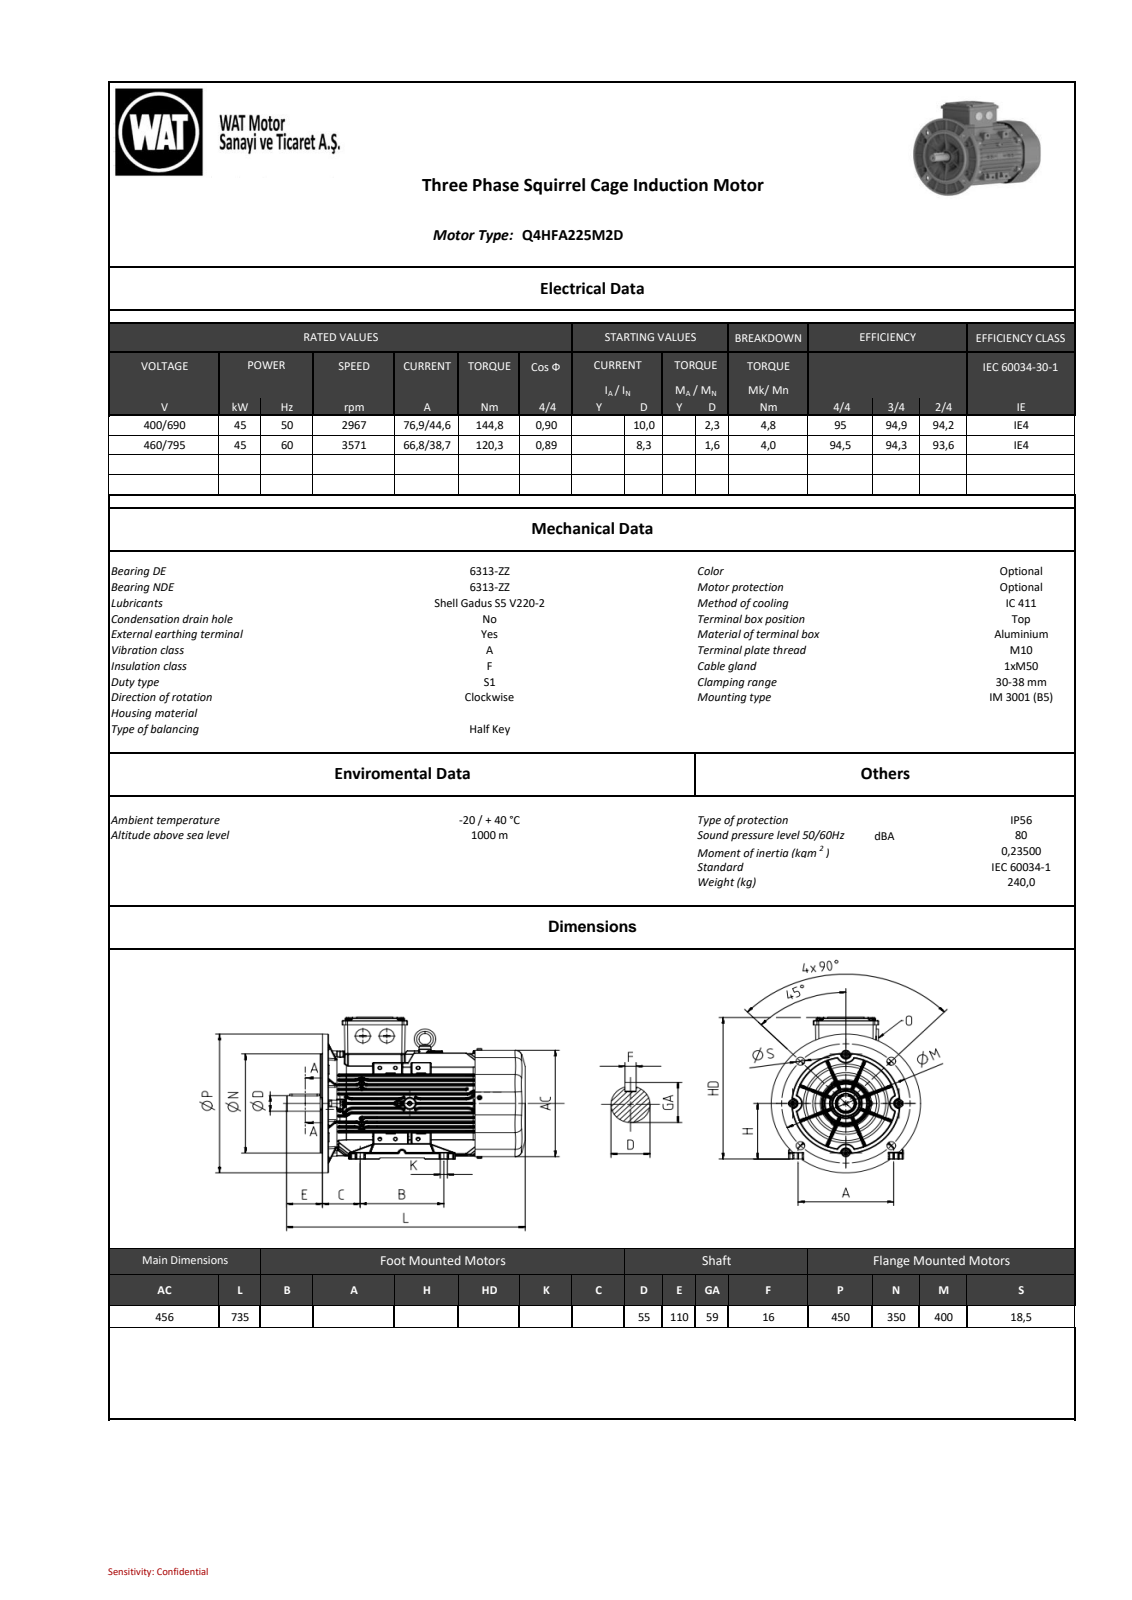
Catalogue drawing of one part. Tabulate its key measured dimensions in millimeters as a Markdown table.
| quantity | value |
| --- | --- |
| part name | AB_objects |
| STEP written by | SIEMENS PLM Software NX2206.8101 (AUTOMOTIVE_DESIGN) |
| units | millimeters |
| bodies | 0 solids, 14197 faces (6160 planar, 2711 cylindrical, 5326 other) |
| overall size | 735 × 507.5 × 450 |
| round holes (diameter × count) | 19 × 8, 0.7 × 6, 6 × 5, 7.5 × 5, 4.3 × 4, 5.5 × 4, 6.5 × 4, 8.38 × 4, 10.5 × 4, 19.5 × 4, 4 × 3, 5 × 3 |
| round bosses / shafts (diameter × count) | 10 × 6, 16.5 × 4, 16 × 4, 5.85 × 3, 58 × 2, 55.1 × 2, 52.3 × 2, 52.2 × 2 |
| partial cylindrical surfaces (radius × count) | 1 × 619, 2 × 408, 0.2 × 332, 0.5 × 154, 5 × 81, 2.5 × 76, 3 × 48, 4 × 48 |
| main face-to-face distances | 189.81, 15.53, 169.04, 20.77, 14.83, 5.24, 184.57, 24.63, 150.23, 39.58 |
| hole center spacings | 7.4, 156, 146.34, 282.85, 68.18, 82.67, 200.01, 231.52 |
